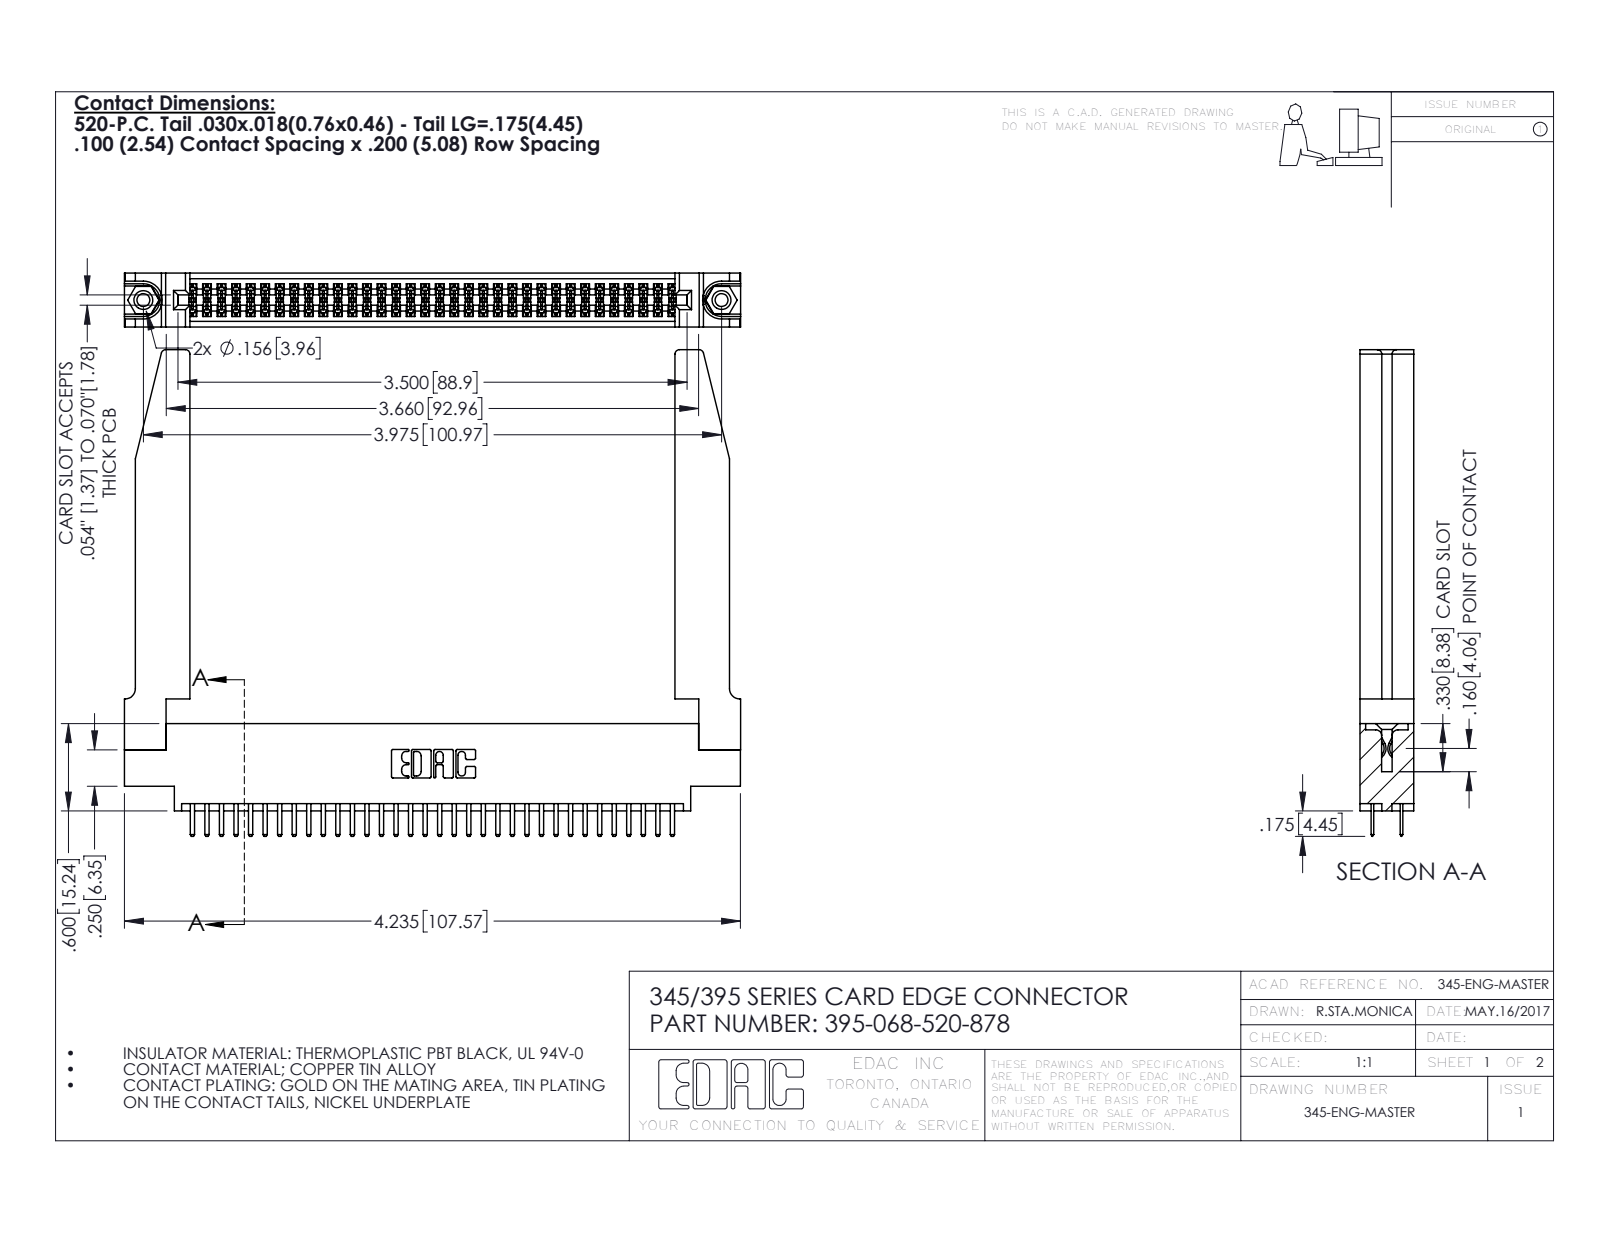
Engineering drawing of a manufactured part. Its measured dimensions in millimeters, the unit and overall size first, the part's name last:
Units: millimetres
Overall size (bounding box): 107.6 × 85 × 9.4
Round holes (diameter × count): ⌀2.3 ×2, ⌀3.2 ×2, ⌀4 ×2, ⌀1.6 ×1
Round bosses / shafts (diameter × count): ⌀3.9 ×2
Partial cylindrical surfaces — rounded edges, fillets, slot ends (radius × count): R0.2 ×102, R0.3 ×72, R0.3 ×22, R0.8 ×8, R0.2 ×6, R0.8 ×6, R0.7 ×3, R0.4 ×2
Main face-to-face distances: 9.4, 1.8, 7.6, 5.1, 2.5, 6.9, 0.6, 5.7, 0.6, 4.4
Hole centre spacings: 6.9, 95, 101
Volume: 18 010 mm³ · Surface area: 21 890 mm²
Bodies: 73 solids, 4036 faces (2606 planar, 1378 cylindrical, 52 other)
Part name (STEP PRODUCT): 345-292-001_345-293-120; 345-250-001_345-250-001-102; 345-220-078_345-220-078; 345 Part_0.170 Offset - 0.156 Dia-TH (+1 more)
STEP written by: SolidWorks 2016 (CONFIG_CONTROL_DESIGN)
